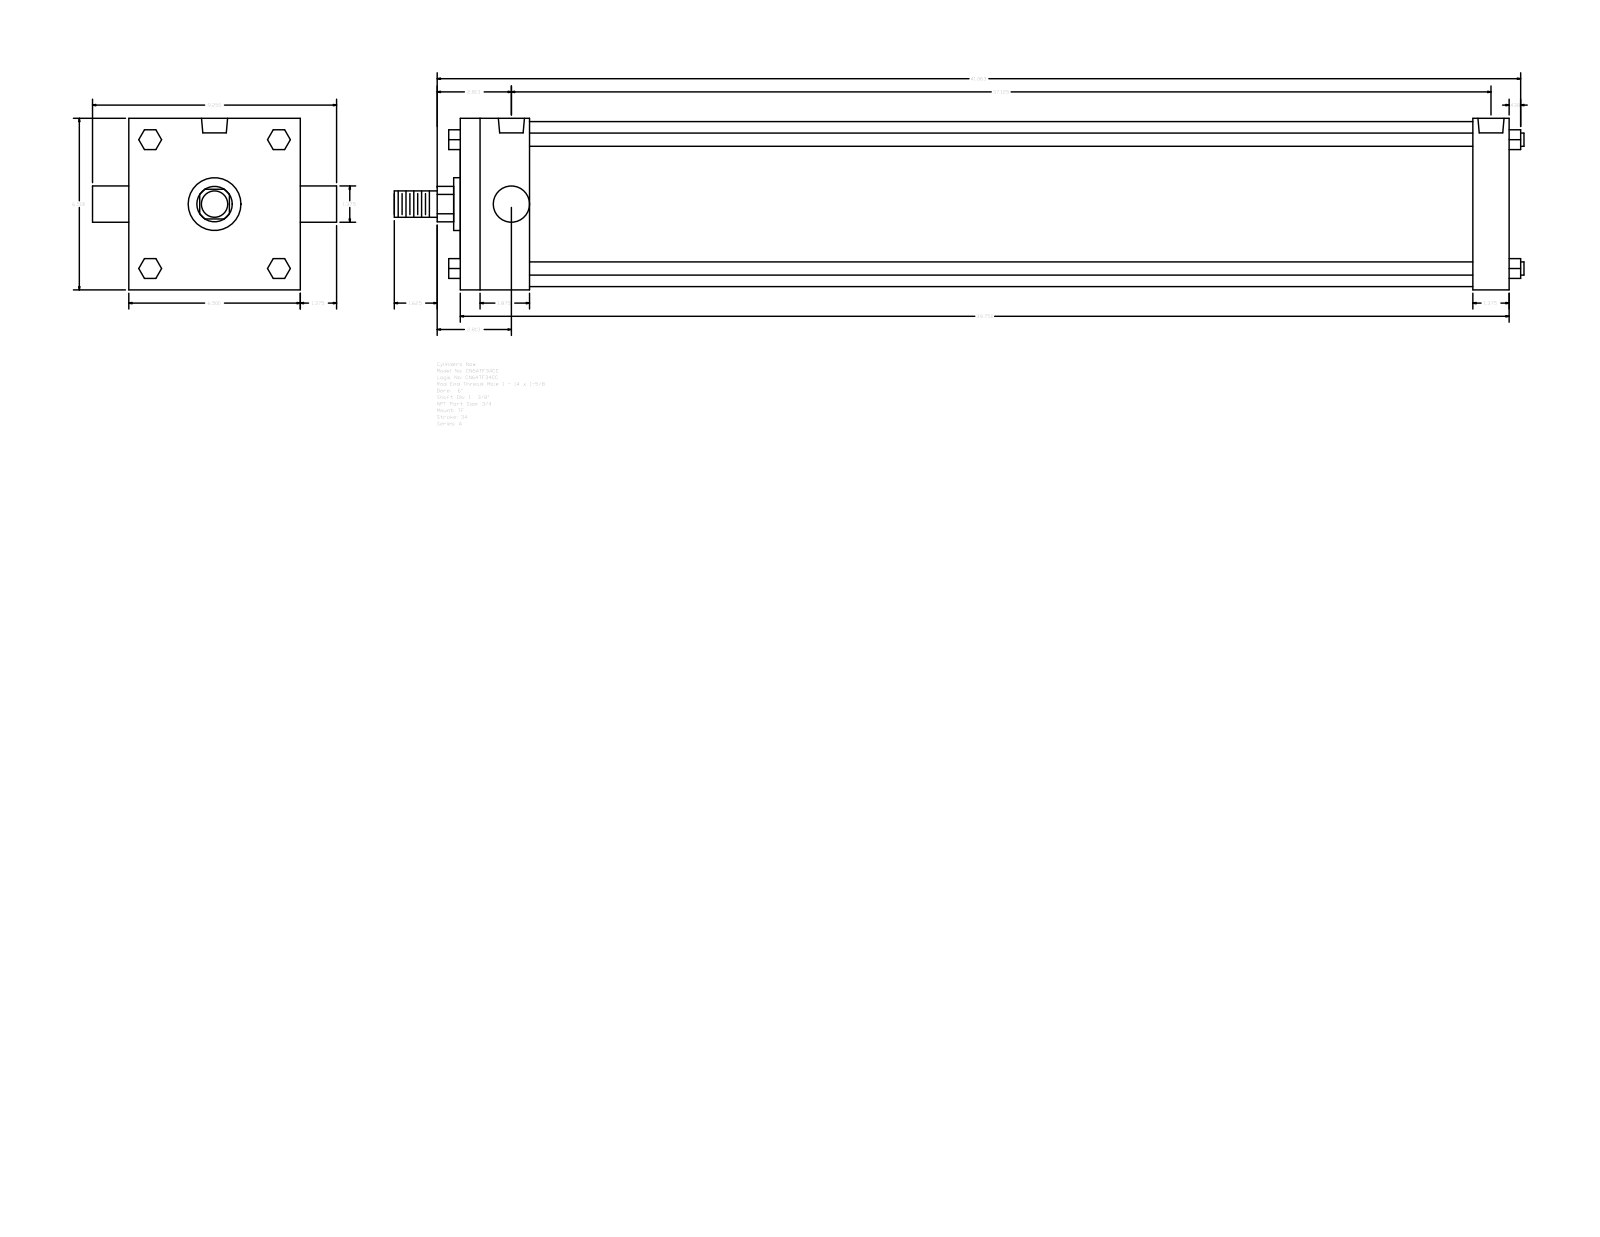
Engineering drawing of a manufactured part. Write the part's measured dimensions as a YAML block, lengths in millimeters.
part_name: "A_TF__0600_1.375"
step_written_by: "GSSL Pune (CONFIG_CONTROL_DESIGN)"
units: millimeters
bodies: {solids: 0, faces: 120, planar: 92, cylindrical: 28, other: 0}
overall_size: [1087.44, 234.95, 165.1]
round_holes:
  - {diameter: 15.08, count: 3}
  - {diameter: 25.12, count: 2}
round_bosses_or_shafts:
  - {diameter: 12.7, count: 4}
  - {diameter: 34.92, count: 2}
  - {diameter: 158.75, count: 1}
  - {diameter: 50.8, count: 1}
  - {diameter: 25.4, count: 1}
partial_cylinders:
  - {radius: 17.06, count: 1}
face_to_face_distances: [165.1, 1009.65, 66.67, 942.98, 974.72, 908.05, 34.93, 19.05, 61.97, 107.34]
hole_center_spacings: [5.56, 937.41, 931.85, 942.97]
